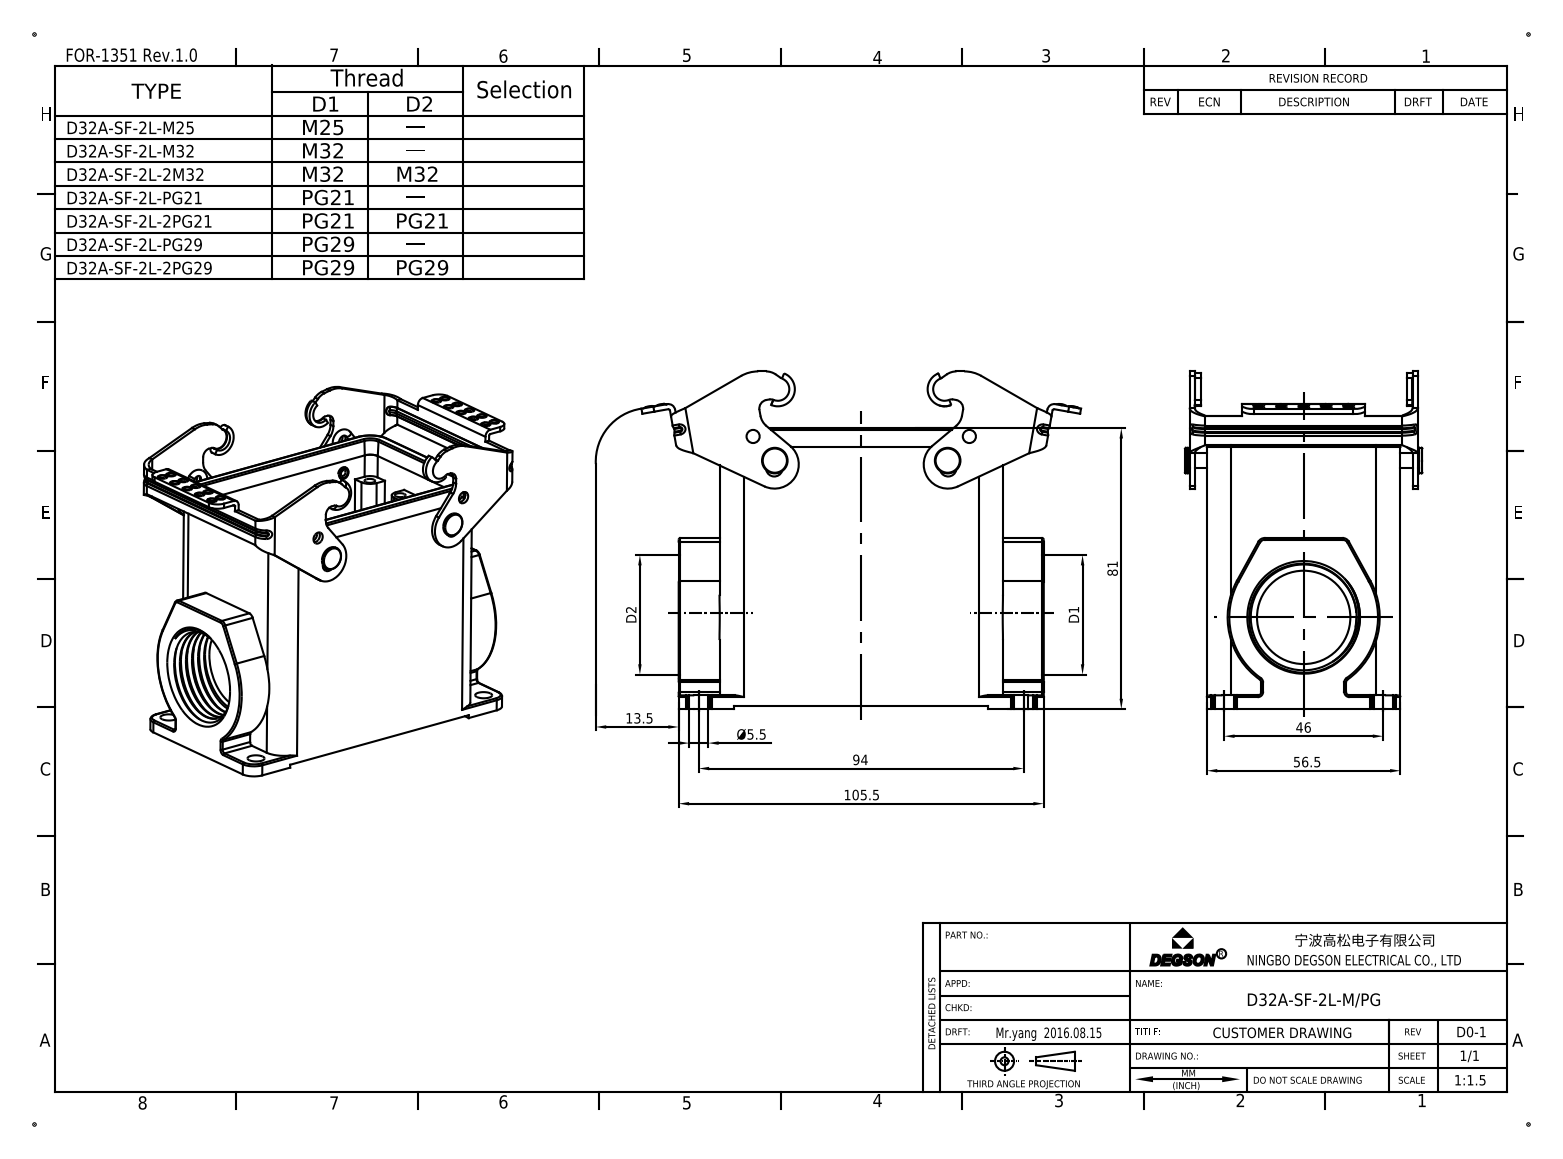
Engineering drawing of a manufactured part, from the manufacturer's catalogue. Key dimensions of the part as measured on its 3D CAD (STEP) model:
Part name (STEP PRODUCT): D32A-SF-2L-MPG
STEP written by: CREO PARAMETRIC BY PTC INC, 2018100 (CONFIG_CONTROL_DESIGN)
Units: millimetres
Bodies: 7 solids, 597 faces (175 planar, 202 cylindrical, 220 other)
Overall size (bounding box): 120.77 × 98.3 × 68.6
Volume: 163 535 mm³ · Surface area: 68 663 mm²
Round holes (diameter × count): ⌀3.5 ×8, ⌀5.5 ×4, ⌀1.8 ×2, ⌀2 ×2, ⌀3 ×2, ⌀29.01 ×1, ⌀30.5 ×1, ⌀33 ×1
Round bosses / shafts (diameter × count): ⌀7.4 ×2, ⌀4.4 ×2, ⌀4.05 ×2
Partial cylindrical surfaces — rounded edges, fillets, slot ends (radius × count): R0.5 ×24, R1.21 ×8, R3 ×8, R4.5 ×8, R2 ×6, R7 ×6, R0.4 ×4, R1 ×4
Main face-to-face distances: 56, 1.5, 4, 64.5, 11.23, 70.77, 3.5, 59.5, 5, 61
Hole centre spacings: 14.2, 16, 23.46, 24, 30.28, 45.1, 66, 67.91
